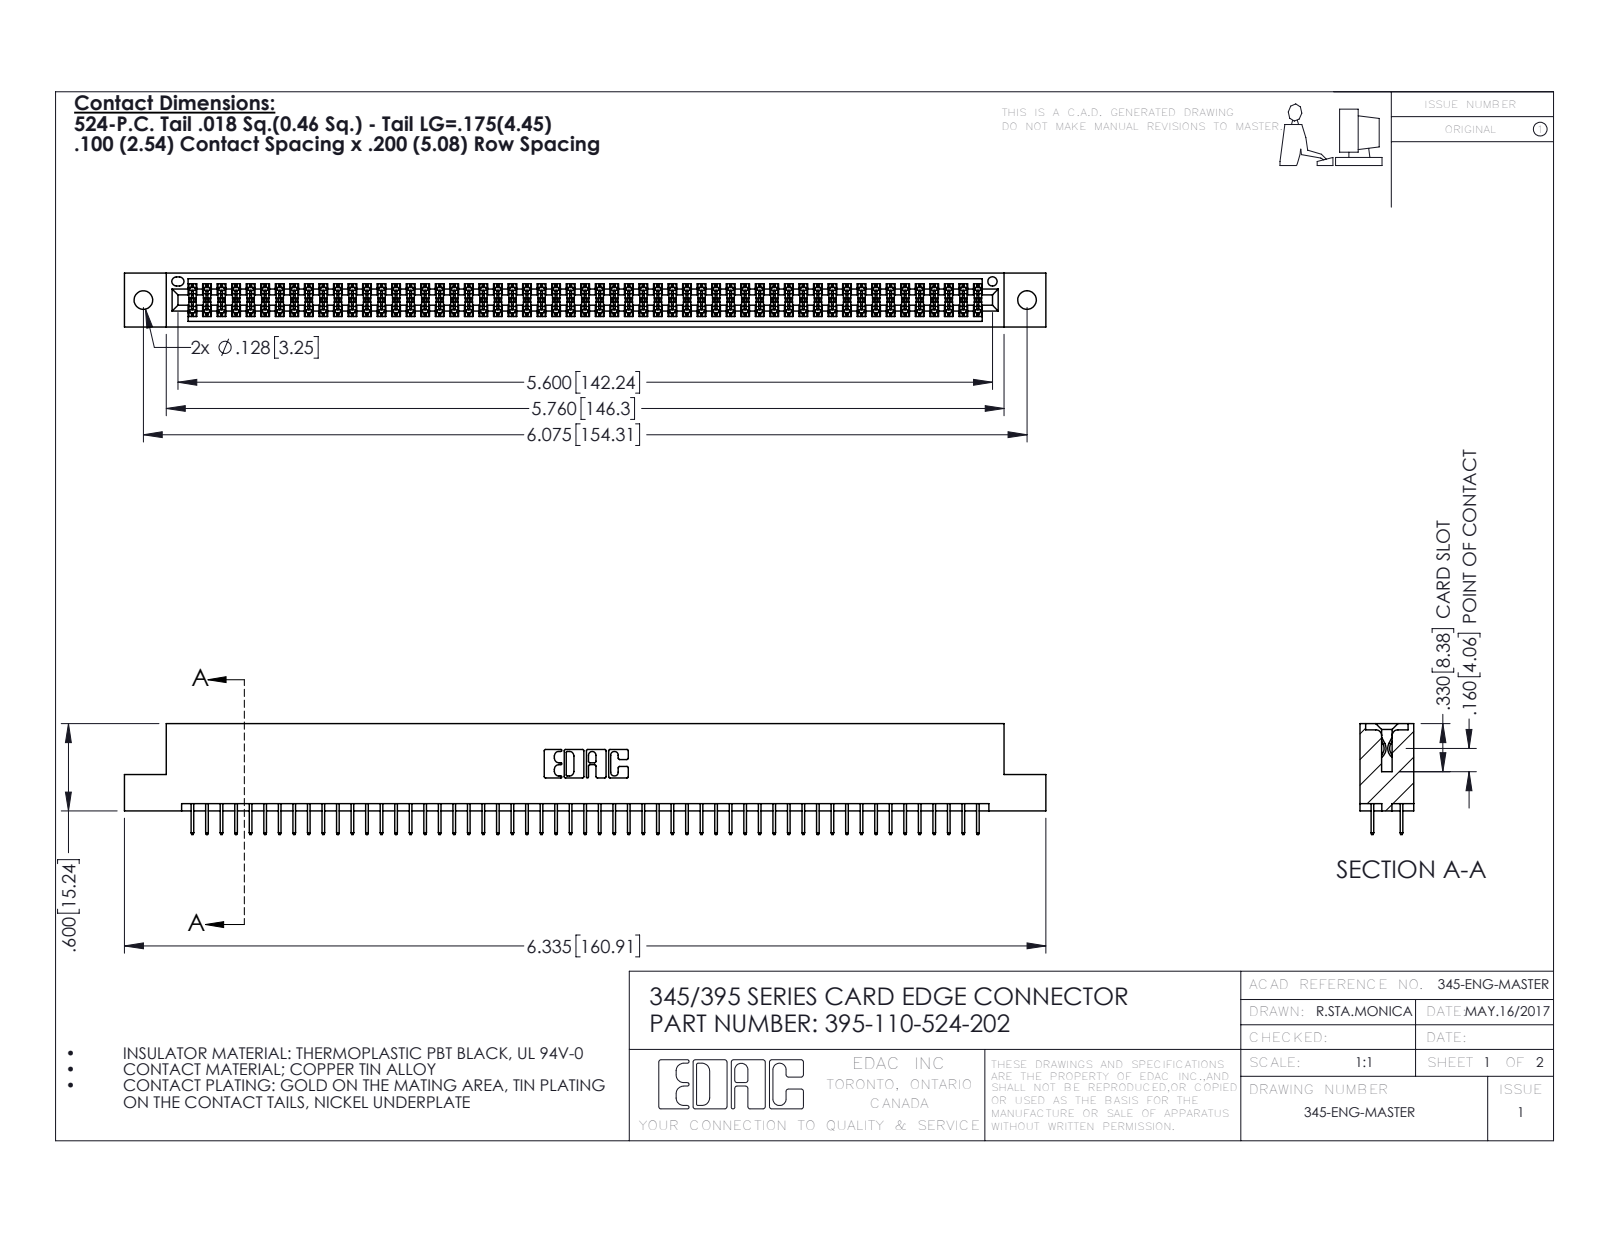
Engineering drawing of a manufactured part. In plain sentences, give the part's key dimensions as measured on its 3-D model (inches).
The part is named "395-110-524-202; 345 Part_Flush Mounting Lugs - 0.128 Dia; 345-292-001_345-293-124". Its 3-D file was written by "SolidWorks 2016 (CONFIG_CONTROL_DESIGN)". It is 111 solids with 6066 faces: 4370 planar, 1696 cylindrical and 0 other. Overall it measures 6.335 by 0.762 by 0.37 inches. Its volume is 0.949 cubic inches and its surface area 34.91 square inches. Round holes: 2 of diameter 0.128, 1 of diameter 0.064. Partial cylindrical surfaces (rounded edges, fillets, slot ends): 165 of radius 0.006, 22 of radius 0.01, 6 of radius 0.007, 6 of radius 0.031, 3 of radius 0.026, 2 of radius 0.014, 2 of radius 0.019, 2 of radius 0.022. The main face-to-face distances are 0.072, 0.298, 0.2, 0.37, 0.098, 0.272, 0.025, 0.225, 0.072, 0.175. The hole center spacings are 0.27, 5.839, 6.075.
